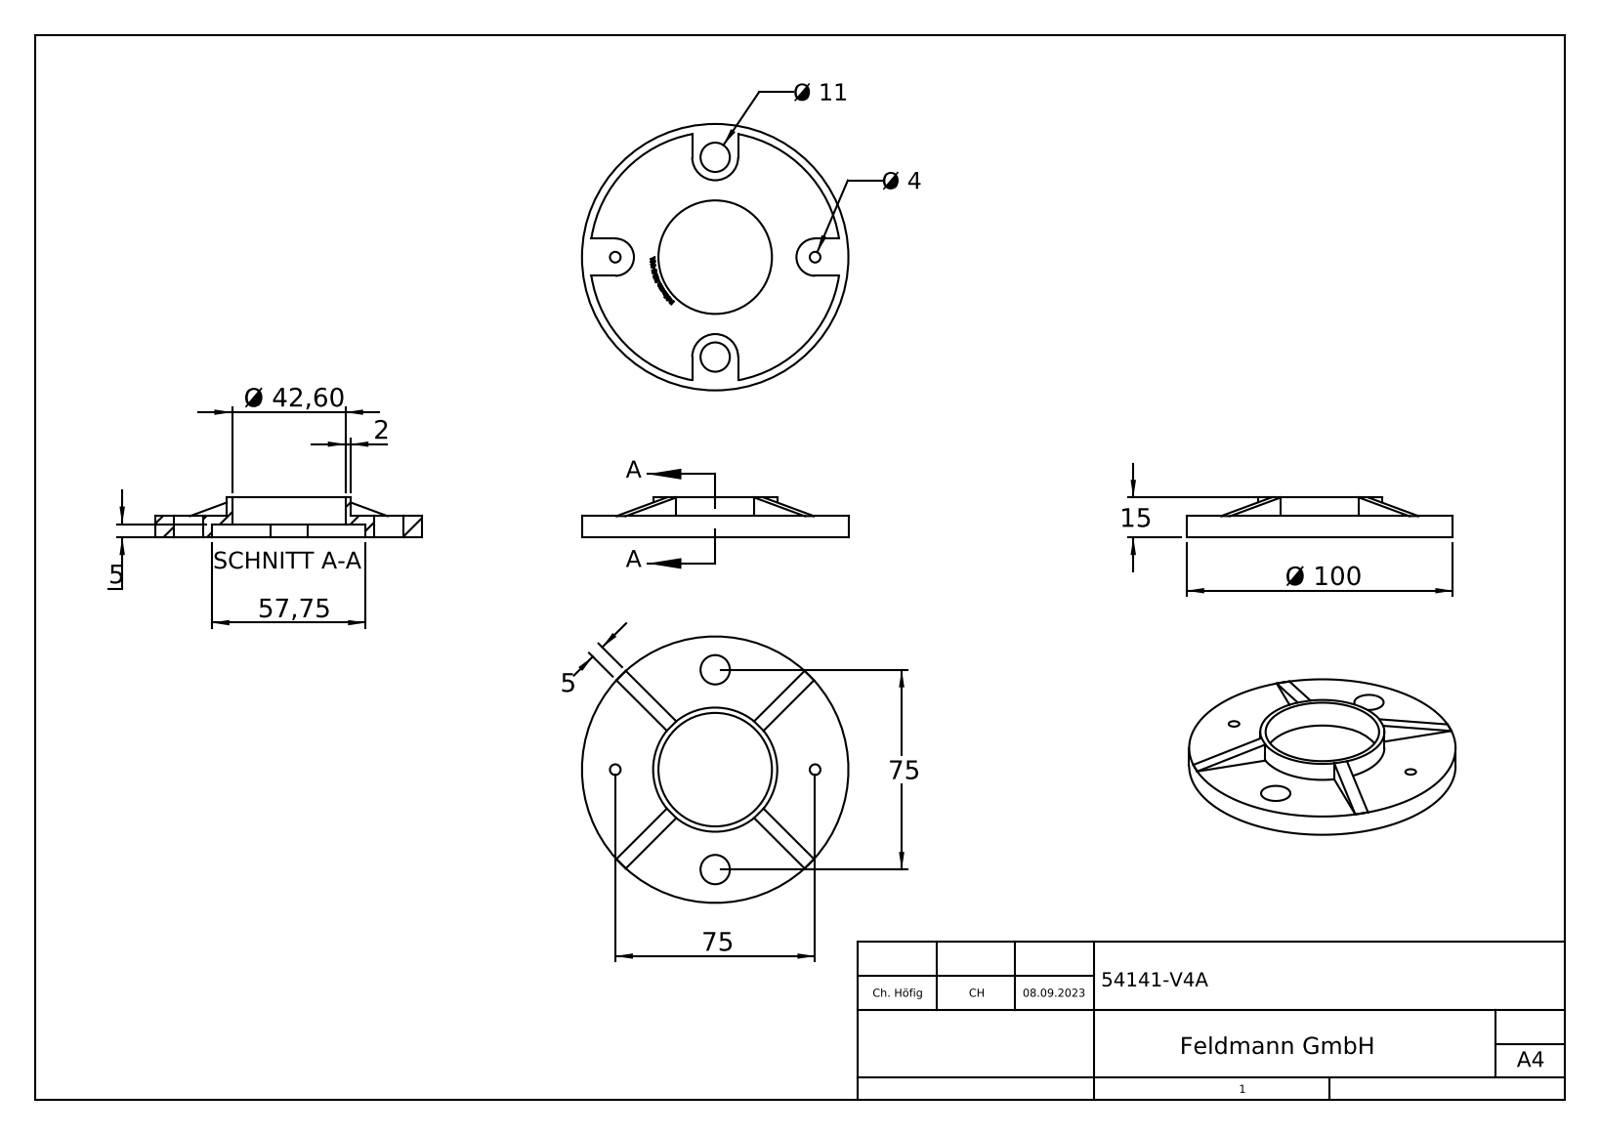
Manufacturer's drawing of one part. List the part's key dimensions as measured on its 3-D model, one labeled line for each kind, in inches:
Part name (STEP PRODUCT): 54141-V4A
STEP written by: SolidWorks 2018 (CONFIG_CONTROL_DESIGN)
Units: inches
Bodies: 1 solid, 262 faces (188 planar, 18 cylindrical, 56 other)
Overall size (bounding box): 3.937 × 3.937 × 0.591
Volume: 1.879 in³ · Surface area: 32.09 in²
Round holes (diameter × count): ⌀0.157 ×2, ⌀0.433 ×2, ⌀1.677 ×1
Round bosses / shafts (diameter × count): ⌀3.937 ×1, ⌀1.835 ×1
Partial cylindrical surfaces — rounded edges, fillets, slot ends (radius × count): R0.276 ×2, R0.339 ×2, R1.85 ×1
Main face-to-face distances: 0.118, 0.197, 0.315, 0.591, 0.394, 0.276, 0.551, 0.679, 0.201, 0.114
Hole centre spacings: 1.476, 2.088, 2.953
